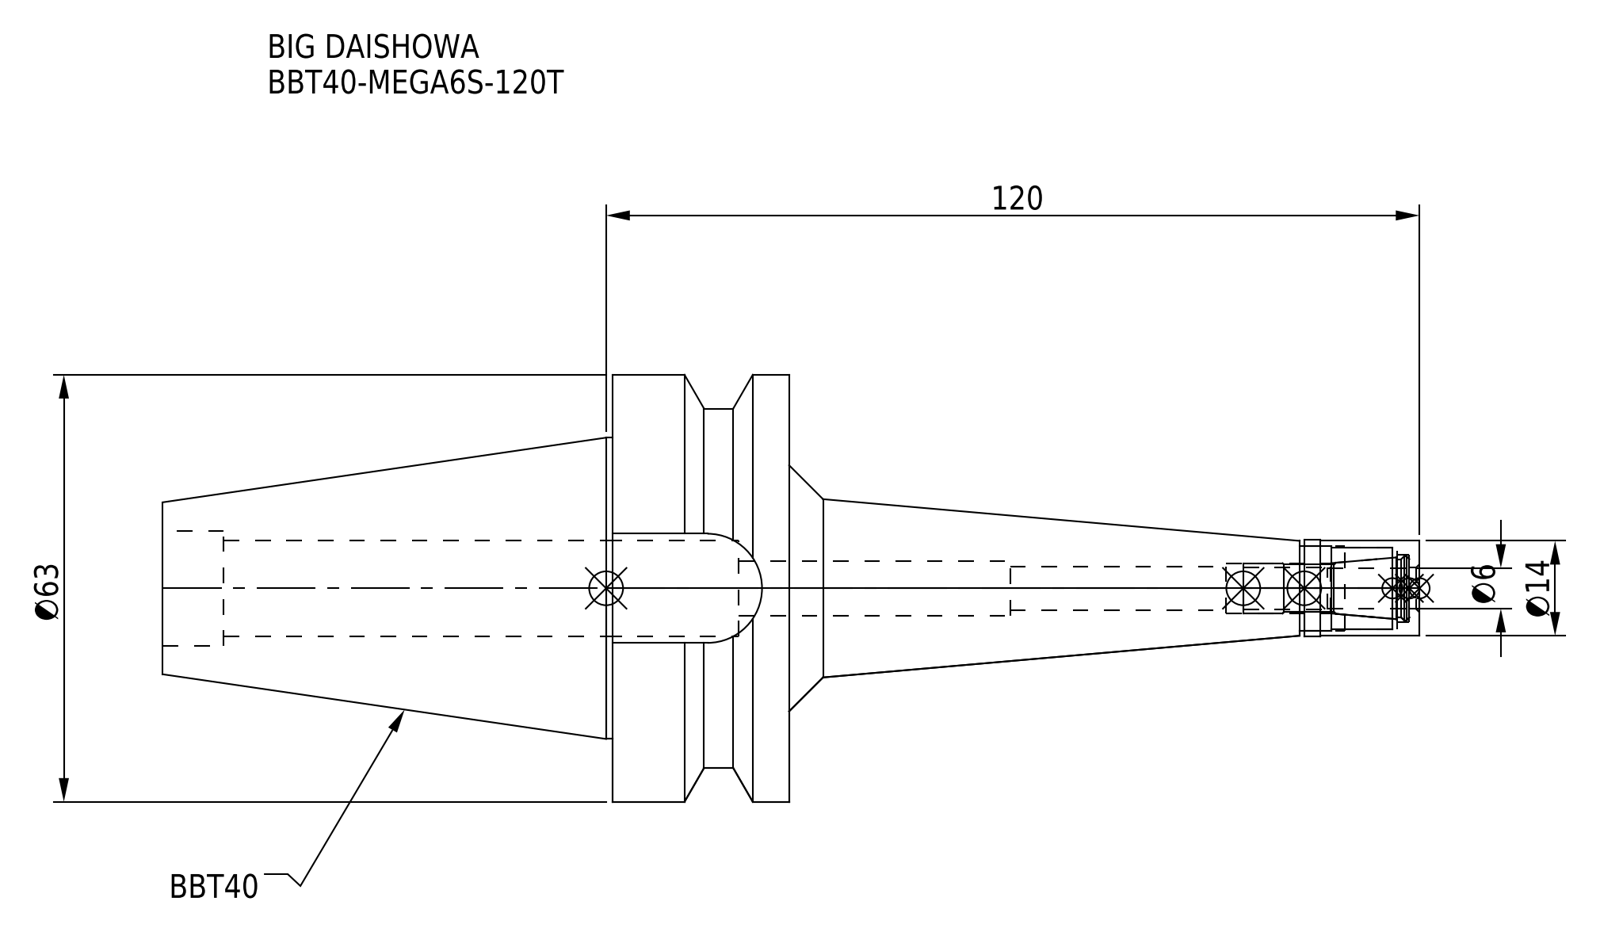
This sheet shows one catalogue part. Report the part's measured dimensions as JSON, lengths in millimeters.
{"part_name": "BBT40-MEGA6S-120T-060.stp; BBT40-MEGA6S-120T_1.stp; BBT40-MEGA6S-120T; BBT40MS06120T-060_ASM.stp (+3 more)", "step_written_by": "SolidWorks 2019 (CONFIG_CONTROL_DESIGN)", "units": "millimeters", "bodies": {"solids": 2, "faces": 74, "planar": 22, "cylindrical": 38, "other": 14}, "overall_size": [185.4, 63, 63], "volume_mm3": 146746, "surface_area_mm2": 31262, "round_holes": [[6.1, 1], [6.4, 1], [7.4, 1], [8, 1], [10, 1], [12, 1], [12.5, 1], [14.2, 1], [17, 1]], "round_bosses_or_shafts": [[63, 1], [53, 1], [44.45, 1], [14.3, 1], [14, 1]], "partial_cylinders_radius": [[8.05, 1]], "face_to_face_distances": [26, 45, 92.4, 66.4, 16.1, 93, 119, 185.4, 100.4, 7.4]}
